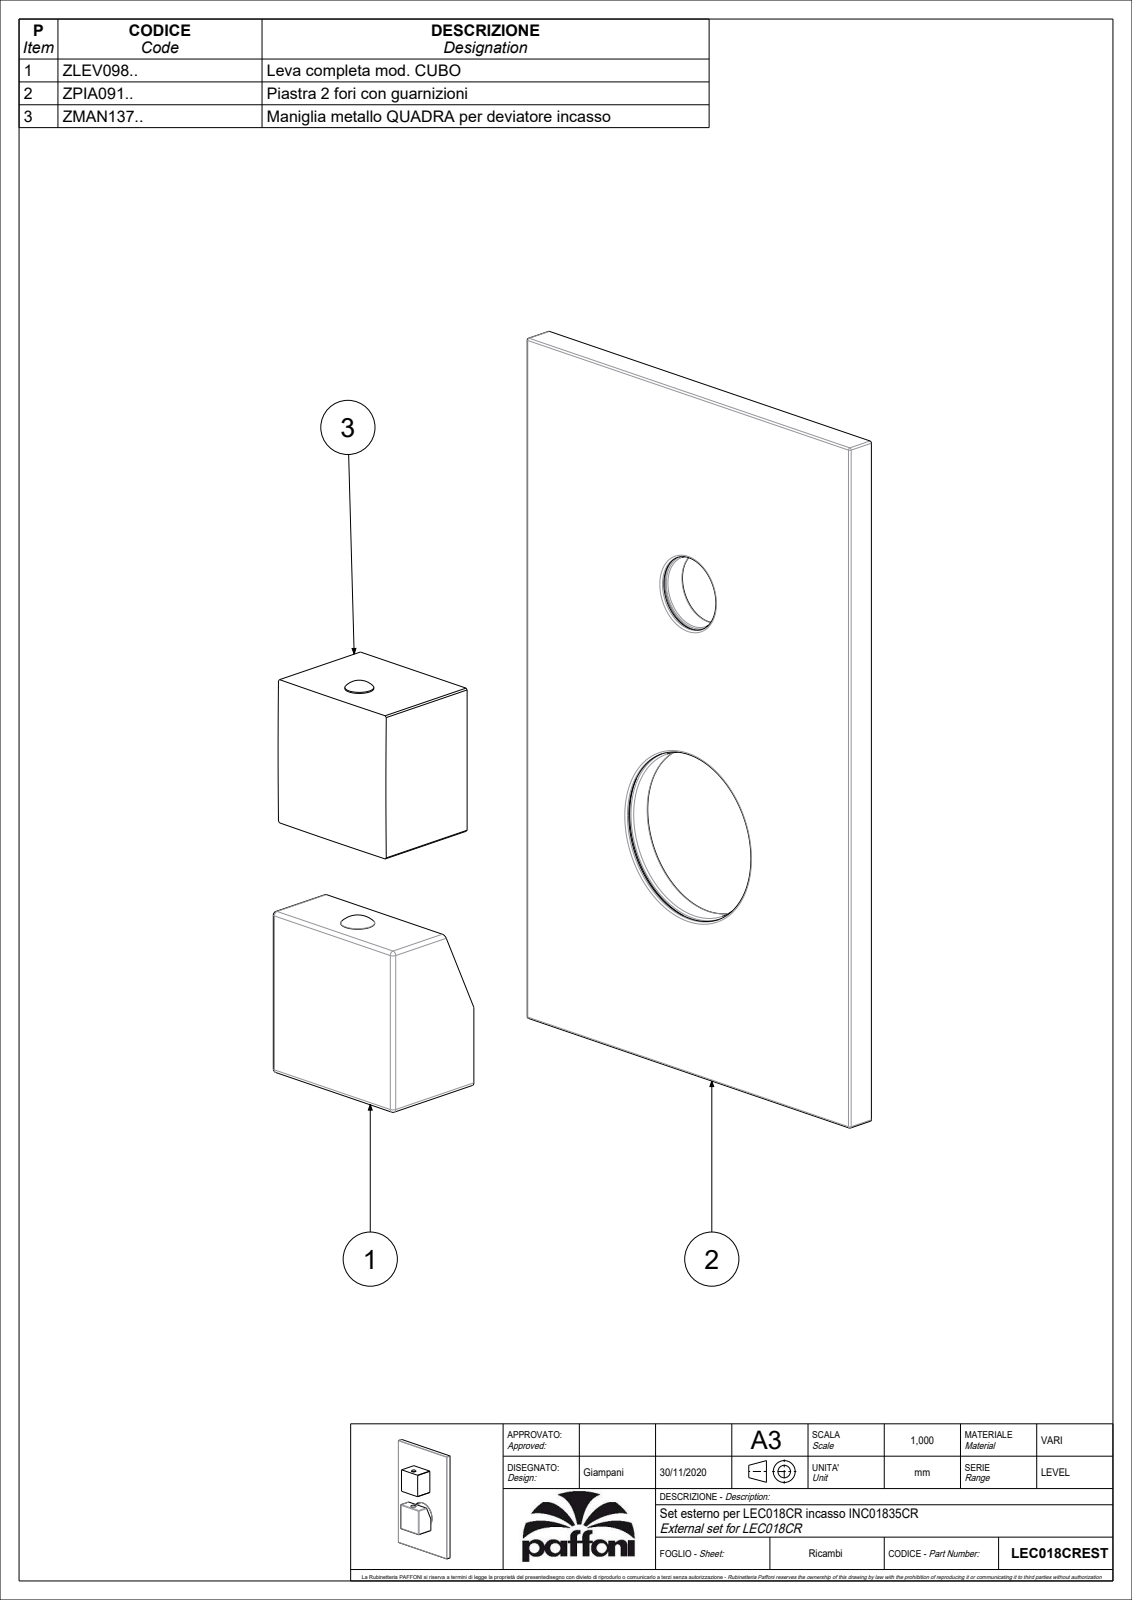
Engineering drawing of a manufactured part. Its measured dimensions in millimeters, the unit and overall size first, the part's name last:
Units: millimetres
Overall size (bounding box): 190 × 120 × 40.49
Round holes (diameter × count): ⌀3 ×1, ⌀3.2 ×1, ⌀4.2 ×1, ⌀5.5 ×1, ⌀6 ×1, ⌀8 ×1, ⌀14.8 ×1, ⌀19.2 ×1, ⌀20 ×1, ⌀21 ×1, ⌀23.2 ×1, ⌀36 ×1
Round bosses / shafts (diameter × count): ⌀5 ×2, ⌀51 ×1, ⌀49 ×1, ⌀25 ×1, ⌀23 ×1, ⌀7.6 ×1
Partial cylindrical surfaces — rounded edges, fillets, slot ends (radius × count): R0.5 ×27, R1 ×24, R28 ×1
Main face-to-face distances: 2.5, 3, 8, 5.5, 0.5, 5, 40, 32, 2, 80
Hole centre spacings: 0.6, 10, 58, 68
Volume: 155 080 mm³ · Surface area: 104 135 mm²
Bodies: 3 solids, 307 faces (109 planar, 122 cylindrical, 76 other)
Part name (STEP PRODUCT): LEC018CREST
STEP written by: CREO PARAMETRIC BY PTC INC, 2020044 (CONFIG_CONTROL_DESIGN)
